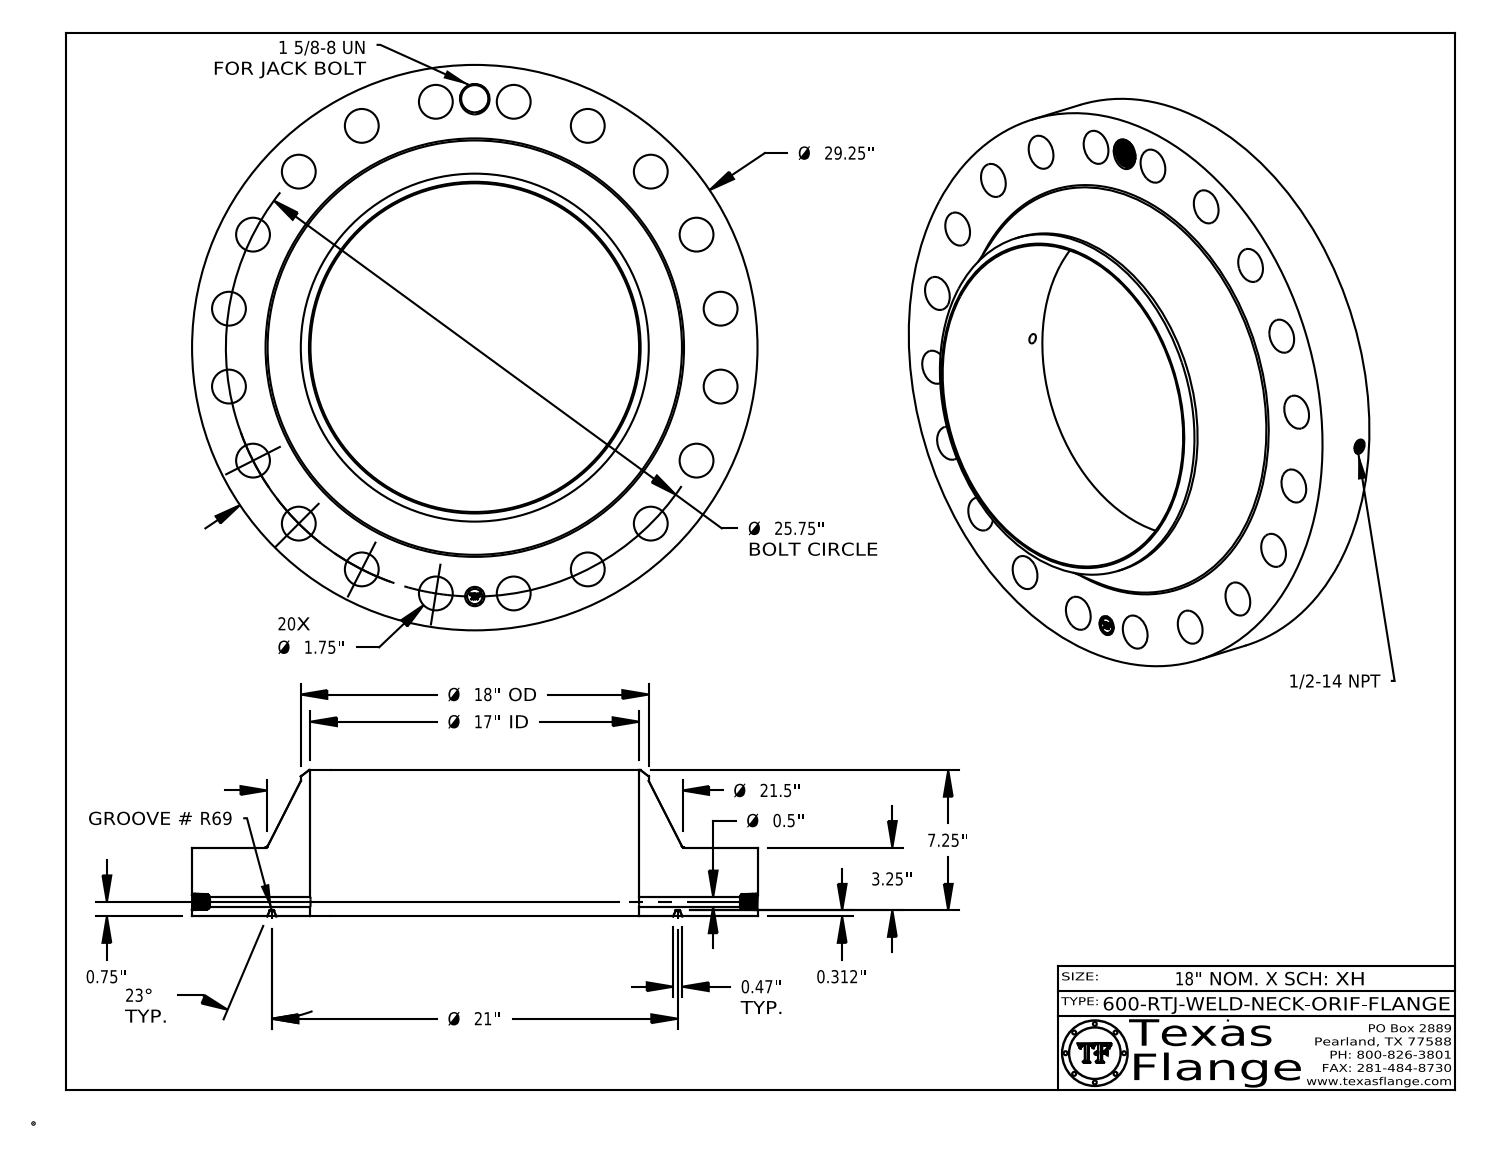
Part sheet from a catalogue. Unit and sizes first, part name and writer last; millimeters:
Units: millimetres
Overall size (bounding box): 743 × 743 × 192.1
Round holes (diameter × count): ⌀44.5 ×20, ⌀12.7 ×1, ⌀17.1 ×1, ⌀25.4 ×1, ⌀35.8 ×1, ⌀431.8 ×1
Round bosses / shafts (diameter × count): ⌀1.5 ×8, ⌀743 ×1, ⌀457.2 ×1, ⌀20 ×1
Main face-to-face distances: 90.5, 7.9, 82.6, 192.1, 184.2, 101.6, 0.4, 90.1, 82.2, 102
Hole centre spacings: 384.4, 622, 646, 327, 296.9, 102.3, 202.1, 462.5
Volume: 27 610 000 mm³ · Surface area: 1 385 000 mm²
Bodies: 1 solid, 881 faces (370 planar, 142 cylindrical, 369 other)
Part name (STEP PRODUCT): 600-RTJ-WELD-NECK
STEP written by: CATIA V5 STEP AP214 (AUTOMOTIVE_DESIGN)
